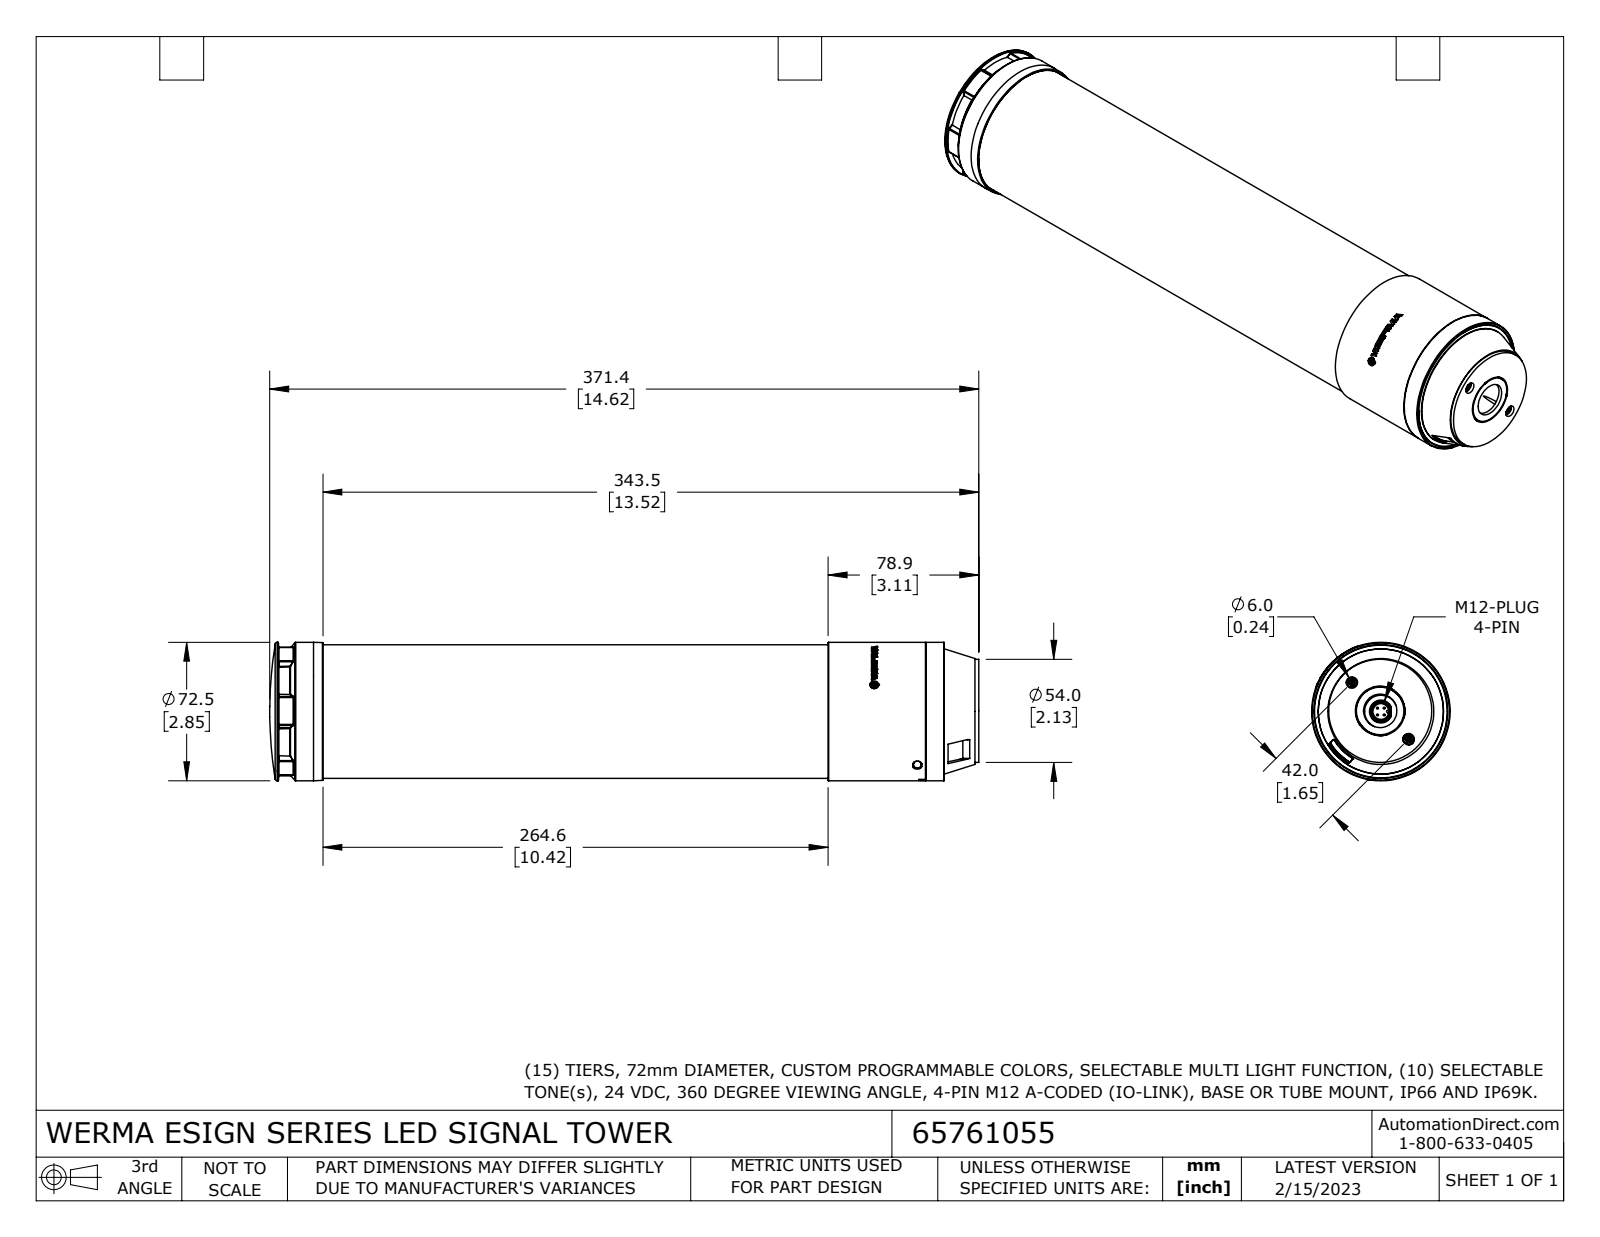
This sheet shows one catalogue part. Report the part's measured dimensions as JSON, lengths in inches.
{"part_name": "65761055", "step_written_by": "SolidWorks 2021 (CONFIG_CONTROL_DESIGN)", "units": "inches", "bodies": {"solids": 1, "faces": 446, "planar": 143, "cylindrical": 96, "other": 207}, "overall_size": [14.621, 2.854, 2.854], "volume_in3": 84.62, "surface_area_in2": 160.5, "round_holes": [[0.236, 2], [0.327, 1], [0.689, 1], [0.711, 1], [1.024, 1]], "round_bosses_or_shafts": [[0.039, 4], [2.854, 1], [2.809, 1], [2.756, 1], [2.126, 1], [0.98, 1], [0.472, 1], [0.413, 1]], "partial_cylinders_radius": [[0.01, 12], [0.028, 12], [0.079, 2], [0.024, 1], [1.244, 1], [1.388, 1], [1.429, 1], [1.437, 1]], "face_to_face_distances": [14.209, 0.079, 14.13, 0.72, 0.641, 13.489, 1.004, 0.925, 0.284, 13.205], "hole_center_spacings": [0.827, 0.019, 0.807, 0.846, 1.654]}
